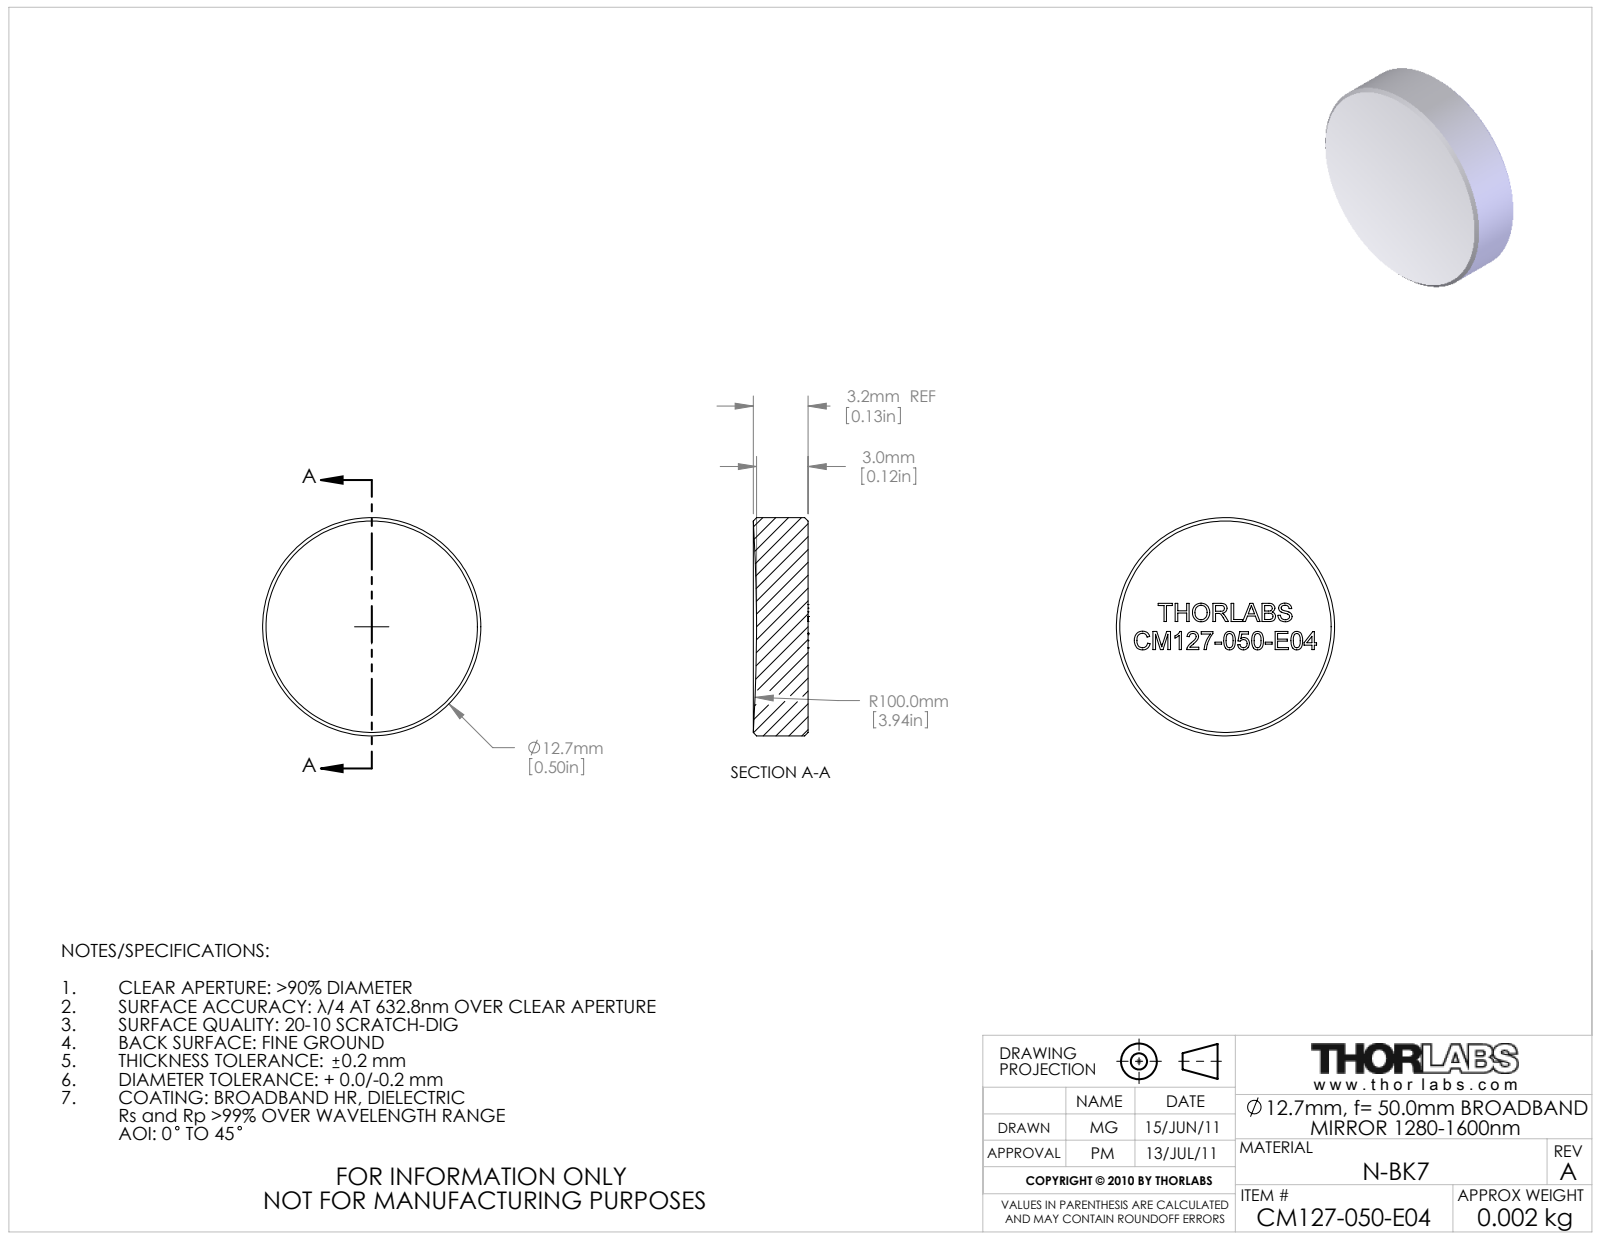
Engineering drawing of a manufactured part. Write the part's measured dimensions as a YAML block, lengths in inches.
part_name: "22655-E0W"
step_written_by: "SolidWorks 2011 (AUTOMOTIVE_DESIGN)"
units: inches
bodies: {solids: 0, faces: 43, planar: 33, cylindrical: 2, other: 8}
overall_size: [0.5, 0.5, 0.126]
round_bosses_or_shafts:
  - {diameter: 0.5, count: 1}
face_to_face_distances: [0.049]
